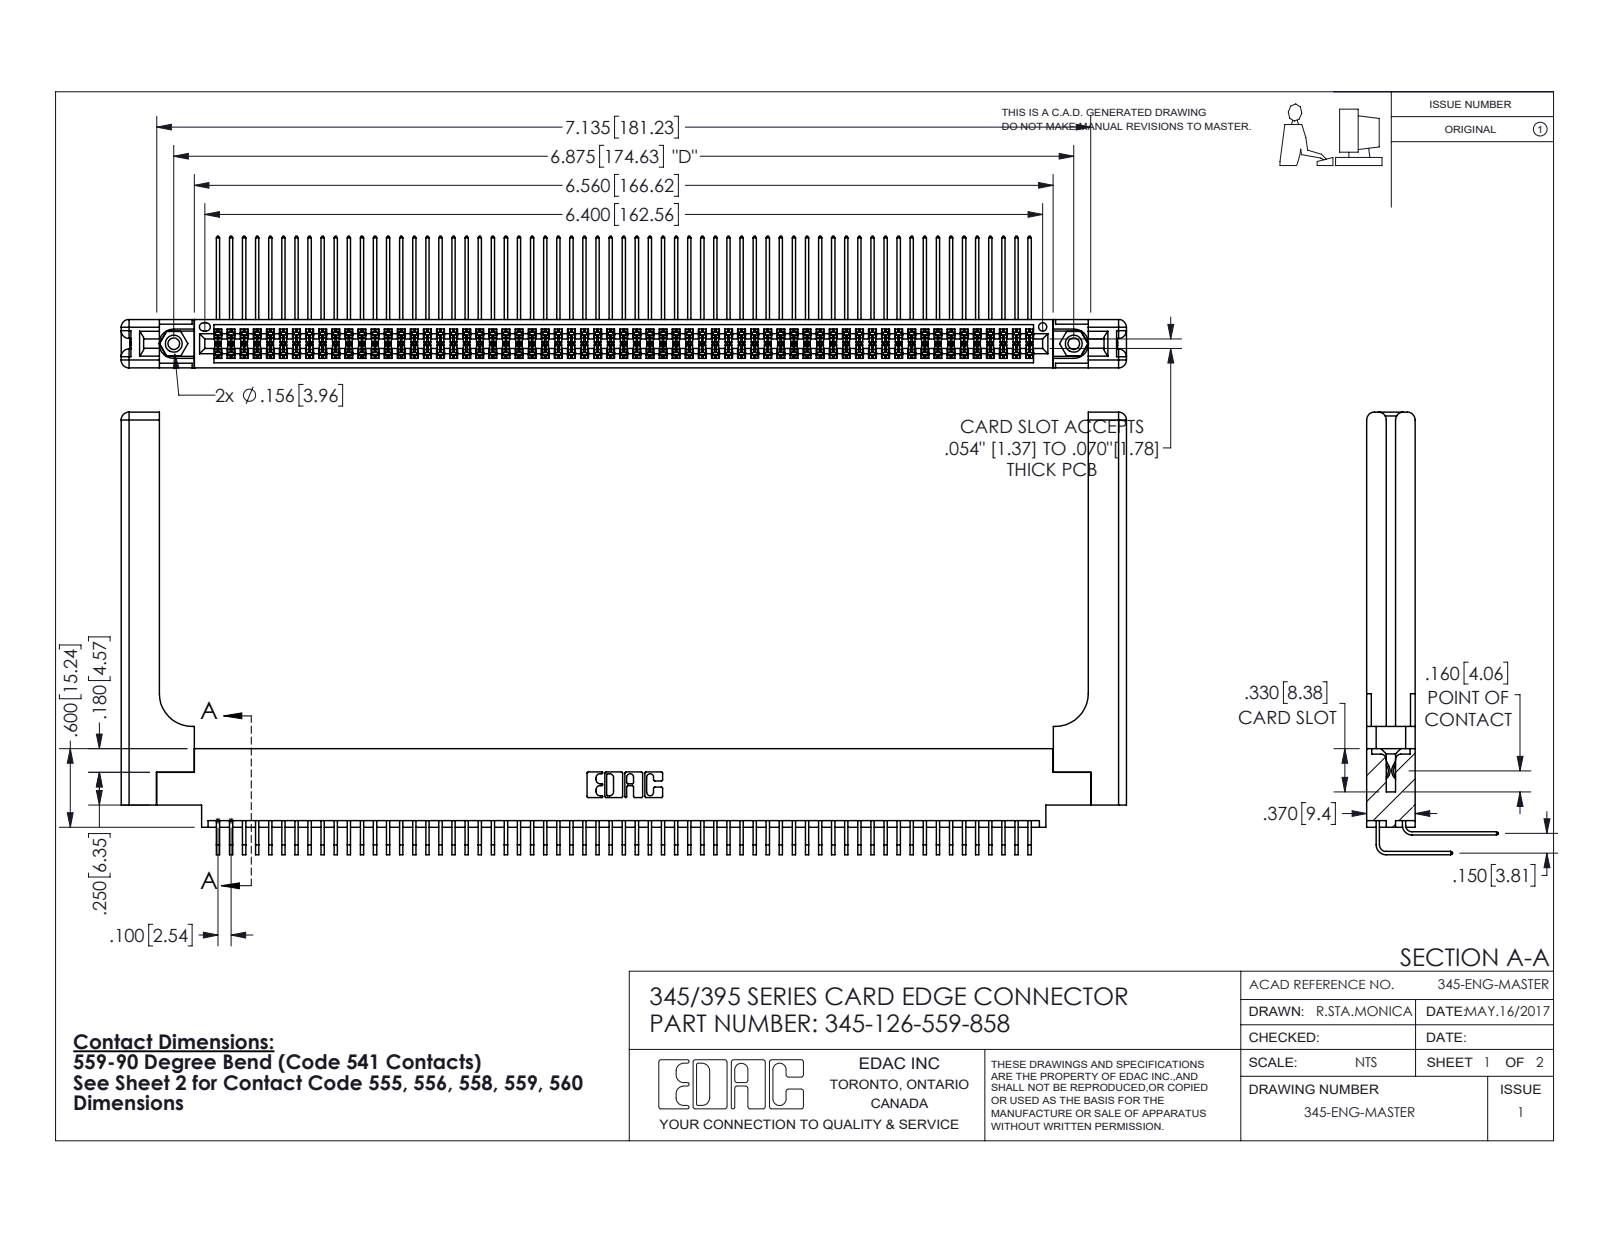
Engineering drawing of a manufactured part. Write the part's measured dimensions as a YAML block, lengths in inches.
part_name: "345-292-001_558 559 Tail - 1; 345-250-001_345-250-001-102; 345-292-001_559 Tail - 2; 345-220-058_345-220-058 (+2 more)"
step_written_by: "SolidWorks 2016 (CONFIG_CONTROL_DESIGN)"
units: inches
bodies: {solids: 131, faces: 6938, planar: 4642, cylindrical: 2236, other: 60}
overall_size: [7.679, 3.379, 1.005]
volume: 1.723
surface_area: 59.25
round_holes:
  - {diameter: 0.089, count: 2}
  - {diameter: 0.125, count: 2}
  - {diameter: 0.156, count: 2}
  - {diameter: 0.064, count: 1}
round_bosses_or_shafts:
  - {diameter: 0.155, count: 2}
partial_cylinders:
  - {radius: 0.006, count: 251}
  - {radius: 0.01, count: 22}
  - {radius: 0.06, count: 16}
  - {radius: 0.007, count: 6}
  - {radius: 0.031, count: 6}
  - {radius: 0.026, count: 3}
  - {radius: 0.014, count: 2}
  - {radius: 0.019, count: 2}
face_to_face_distances: [0.072, 0.298, 0.37, 0.098, 0.272, 0.025, 0.2, 0.225, 0.175, 0.15]
hole_center_spacings: [0.27, 6.639, 6.875]
